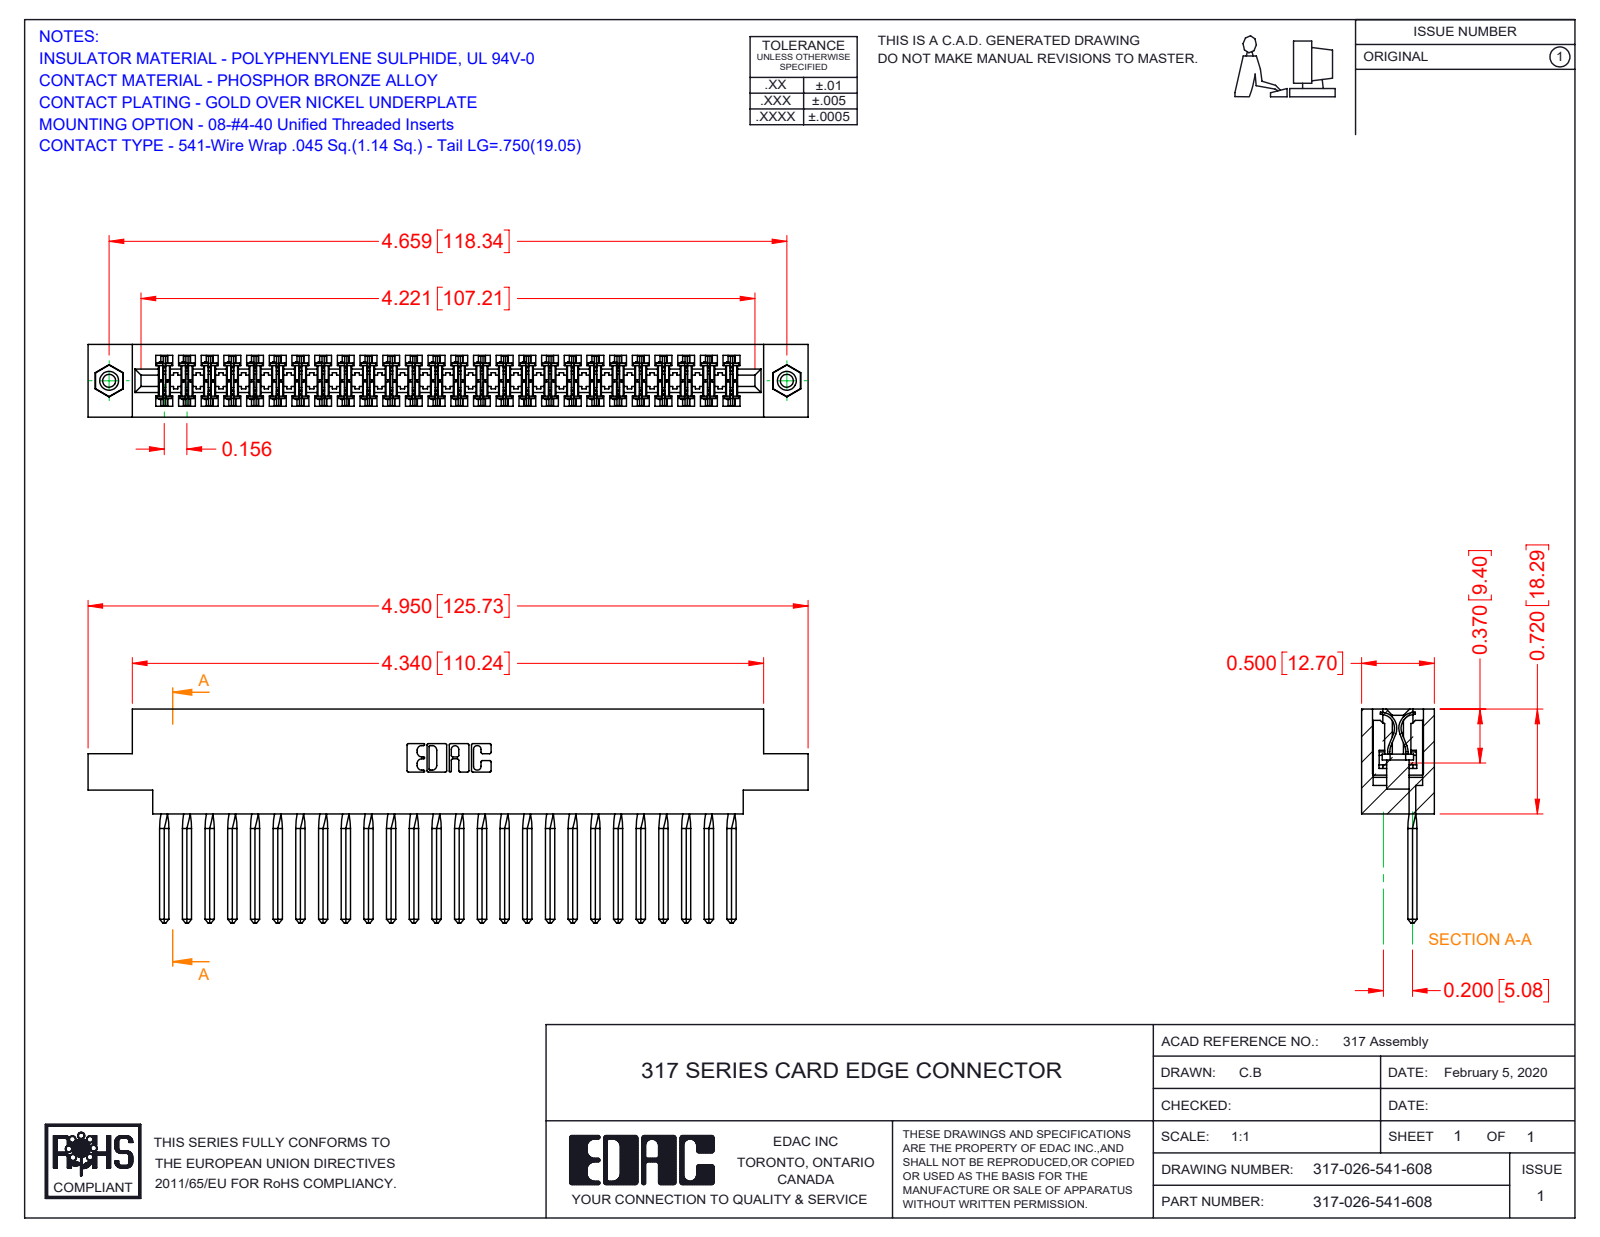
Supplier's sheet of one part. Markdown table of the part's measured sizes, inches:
| quantity | value |
| --- | --- |
| part name | 317 Part_.156 Dia - TI; 317-026-541-608; 345-250-001_345-250-003-102; 317-290-002_541 |
| STEP written by | SolidWorks 2016 (CONFIG_CONTROL_DESIGN) |
| units | inches |
| bodies | 29 solids, 4114 faces (3314 planar, 680 cylindrical, 120 other) |
| overall size | 4.95 × 1.47 × 0.5 |
| volume | 1.214 in³ |
| surface area | 42.77 in² |
| round holes (diameter × count) | 0.089 × 2, 0.125 × 2, 0.156 × 2 |
| round bosses / shafts (diameter × count) | 0.155 × 2 |
| partial cylindrical surfaces (radius × count) | 0.015 × 52, 0.01 × 22, 0.007 × 6, 0.031 × 6, 0.026 × 3, 0.095 × 2, 0.1 × 2, 0.11 × 2 |
| main face-to-face distances | 0.5, 0.075, 0.425, 0.35, 0.11, 0.195, 0.72, 0.136, 0.772, 0.211 |
| hole center spacings | 4.659 |
